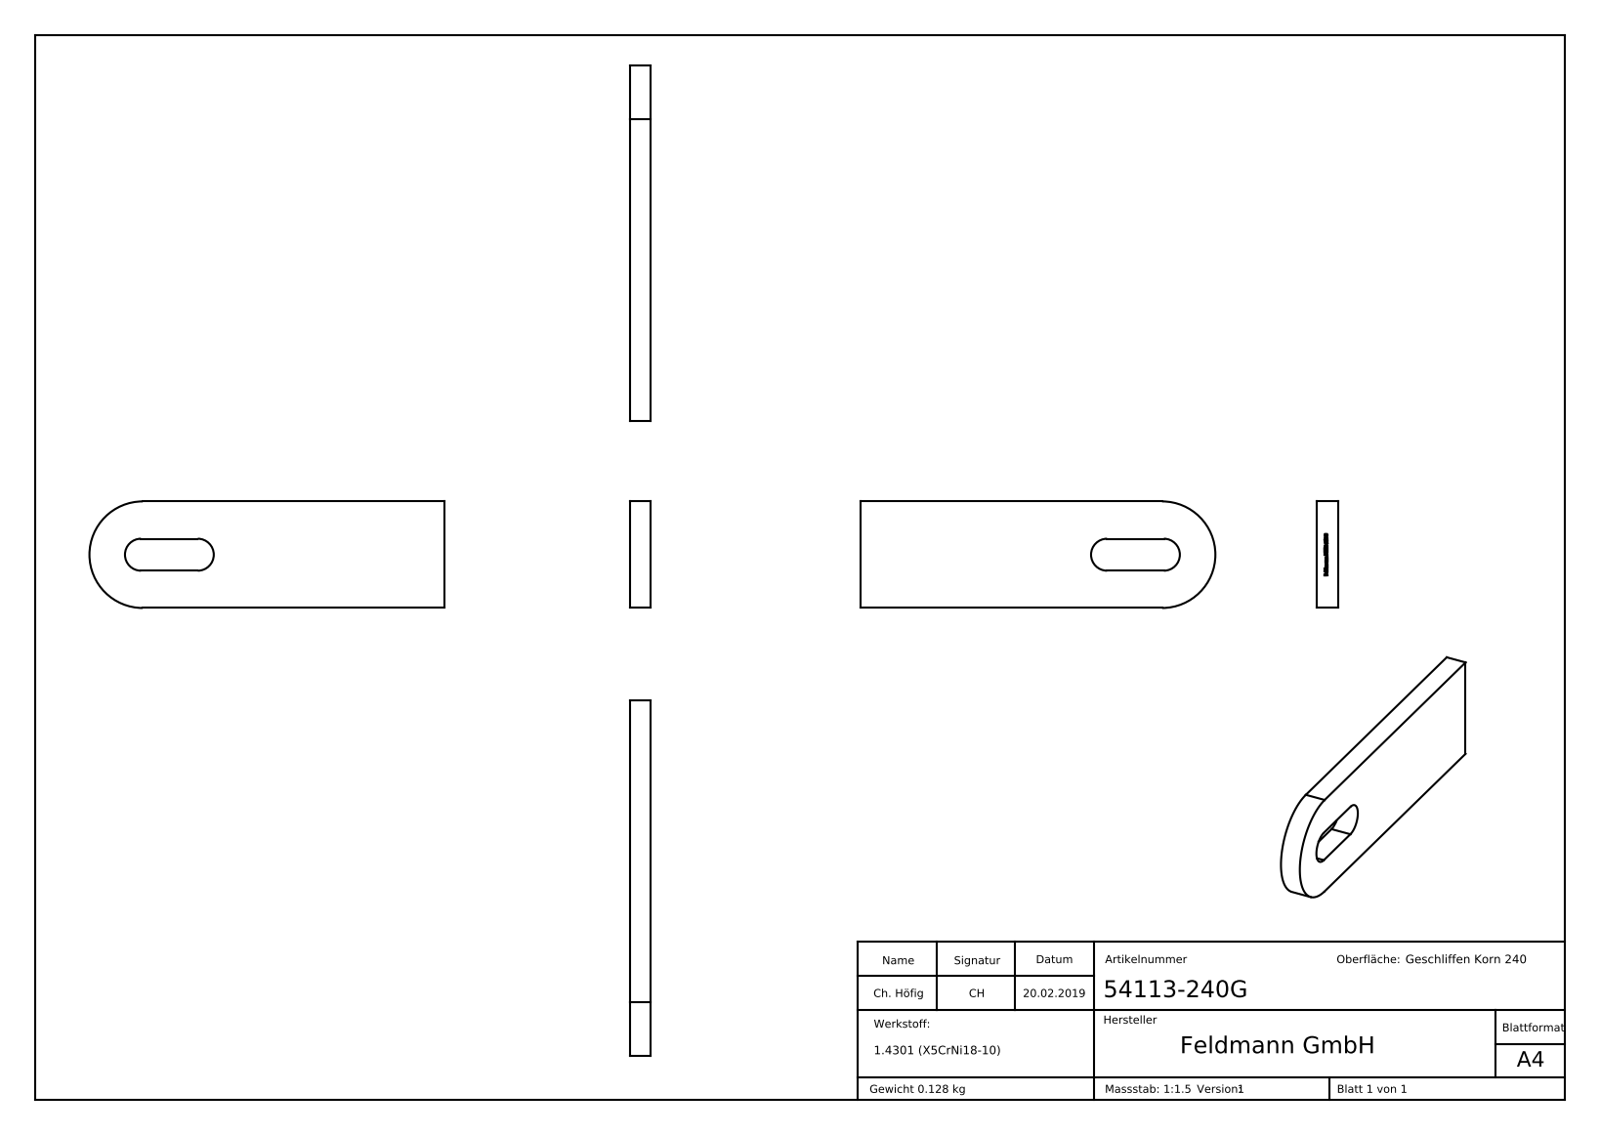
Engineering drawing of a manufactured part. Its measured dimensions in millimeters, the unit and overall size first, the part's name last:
Units: millimetres
Overall size (bounding box): 100 × 30 × 6
Partial cylindrical surfaces — rounded edges, fillets, slot ends (radius × count): R4.5 ×2, R15 ×1
Main face-to-face distances: 6, 30, 10.5, 19.5, 9, 3, 2.82, 0.61, 0.71, 0.53
Volume: 16 175 mm³ · Surface area: 7 242 mm²
Bodies: 1 solid, 245 faces (146 planar, 5 cylindrical, 94 other)
Part name (STEP PRODUCT): 54113-240G
STEP written by: SolidWorks 2015 (CONFIG_CONTROL_DESIGN)
